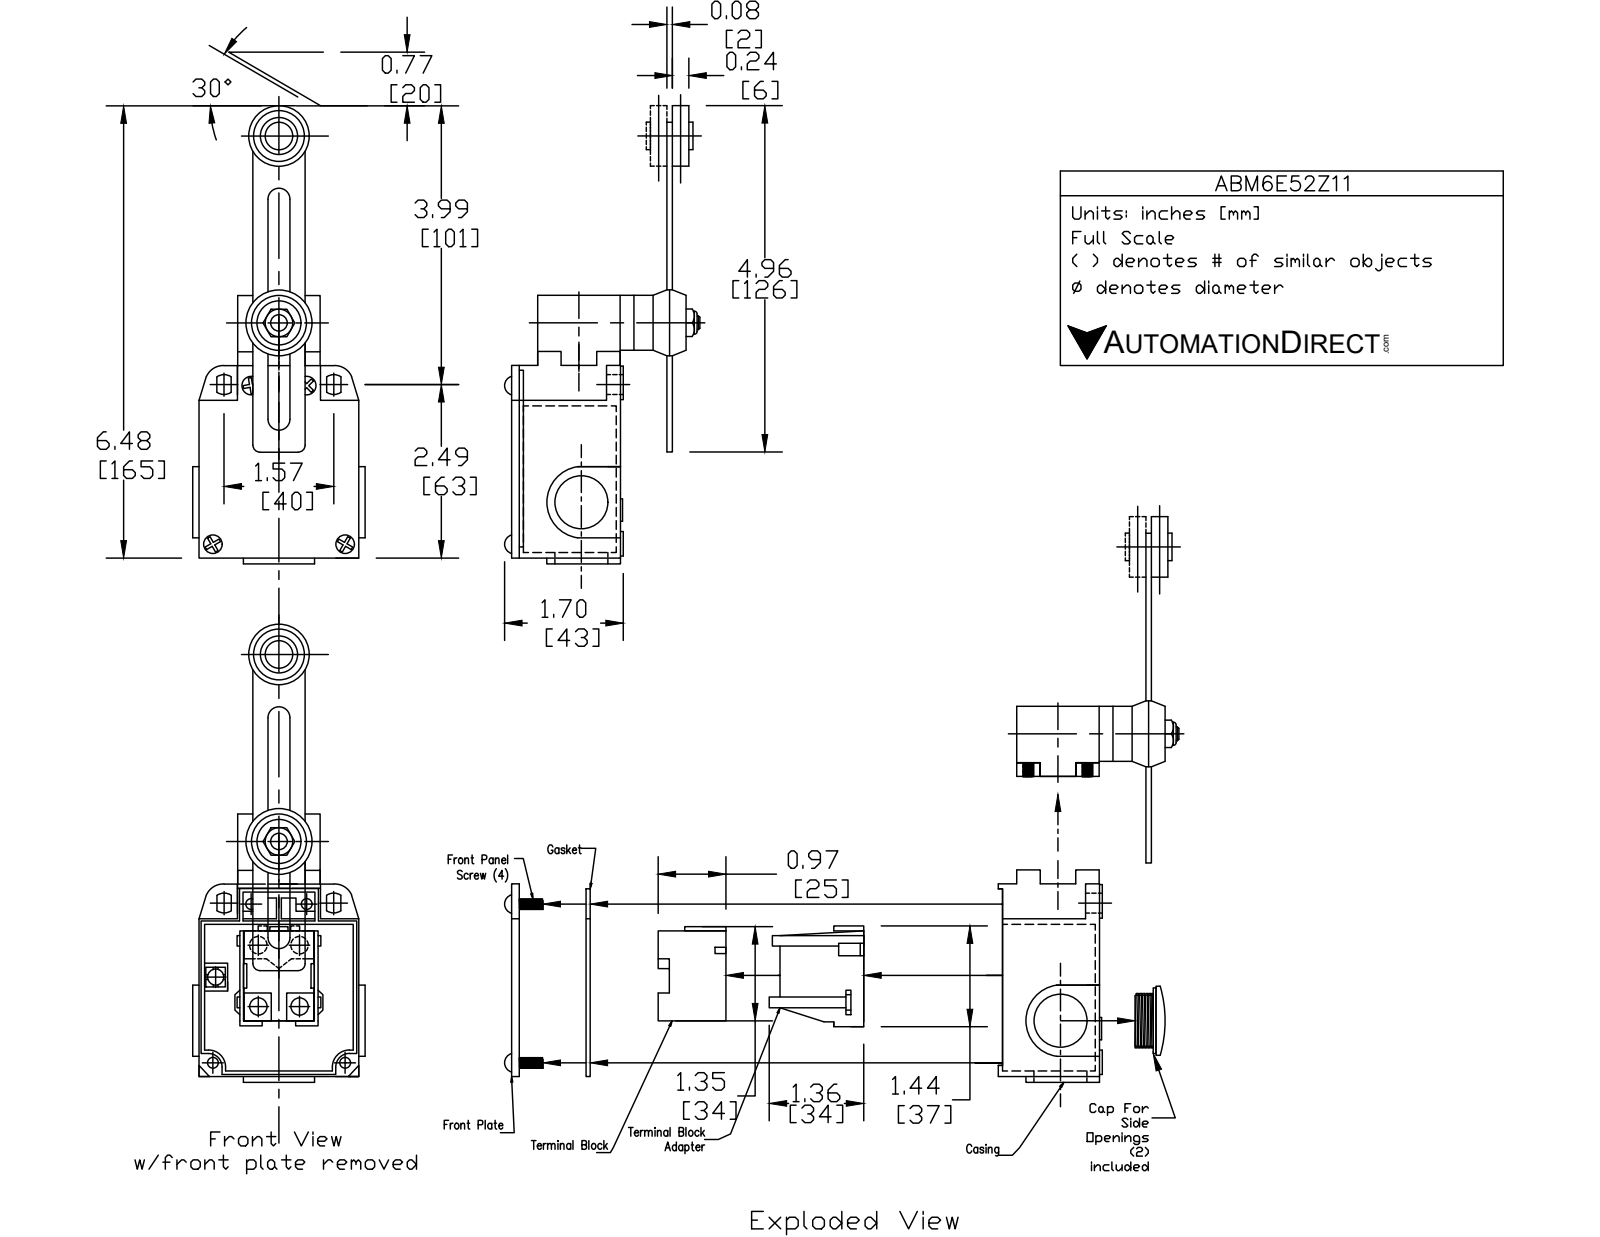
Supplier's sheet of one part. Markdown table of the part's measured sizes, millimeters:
| quantity | value |
| --- | --- |
| part name | ABM6E52Z11 |
| STEP written by | SolidWorks 2017 (AUTOMOTIVE_DESIGN) |
| units | millimeters |
| bodies | 5 solids, 298 faces (140 planar, 113 cylindrical, 45 other) |
| overall size | 161.5 × 62 × 59.7 |
| volume | 183 900 mm³ |
| surface area | 34 620 mm² |
| round holes (diameter × count) | 17 × 2, 19 × 2, 3 × 1, 6 × 1, 14 × 1 |
| round bosses / shafts (diameter × count) | 7 × 5, 12 × 2, 10 × 2, 9 × 2, 24 × 1, 22 × 1, 20 × 1, 11.5 × 1 |
| partial cylindrical surfaces (radius × count) | 1.5 × 12, 1 × 4, 3 × 2, 3.7 × 2, 4 × 2, 6.5 × 2, 13 × 2, 7 × 1 |
| main face-to-face distances | 39.5, 2, 14, 44, 8.2, 47.7, 10.2, 49.7, 58, 30 |
| hole center spacings | 14, 68, 80.4 |
